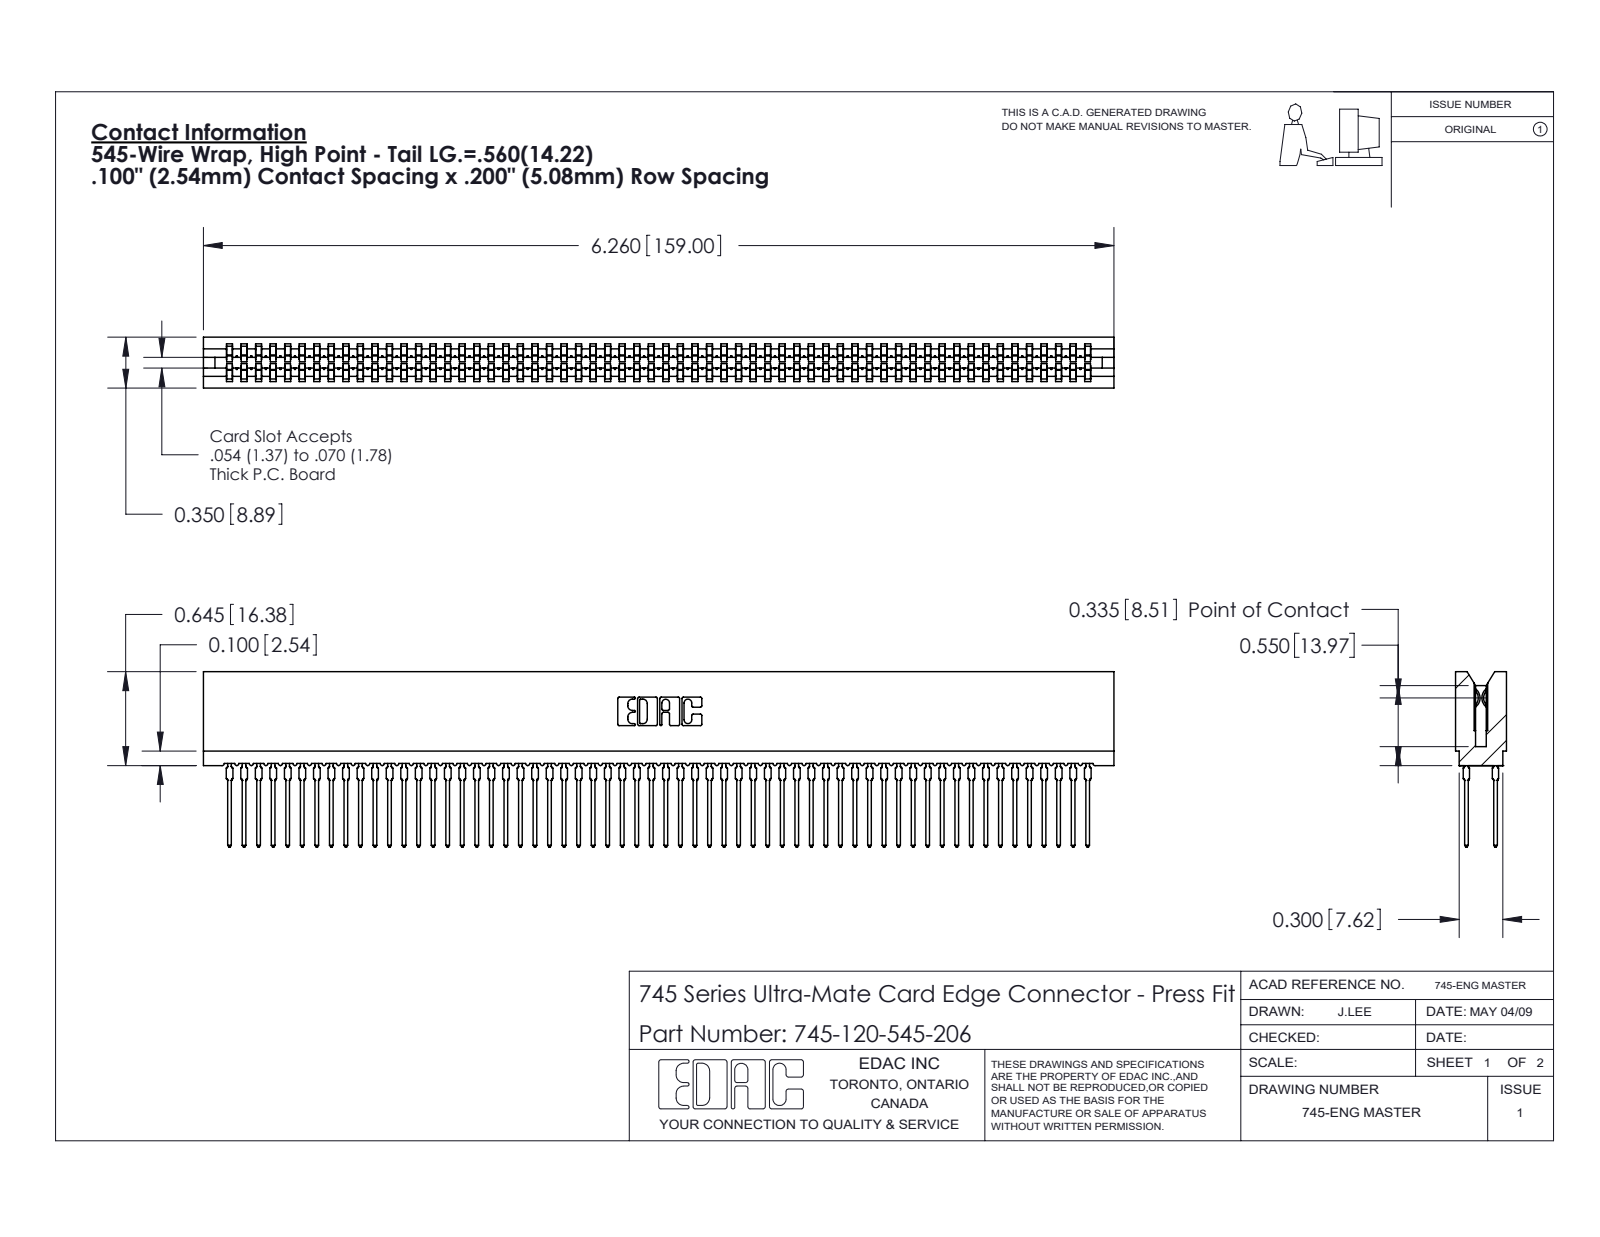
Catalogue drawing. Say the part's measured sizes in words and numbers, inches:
The part is named "745-292-001_545; 745-120-545-206; 745 Part_Insulator Option - 06". Its 3-D file was written by "SolidWorks 2020 (CONFIG_CONTROL_DESIGN)". It is 121 solids with 10836 faces: 5576 planar, 2140 cylindrical and 3120 other. Overall it measures 6.26 by 1.206 by 0.35 inches. Its volume is 0.892 cubic inches and its surface area 49.56 square inches. Partial cylindrical surfaces (rounded edges, fillets, slot ends): 240 of radius 0.021, 120 of radius 0.015, 22 of radius 0.01, 8 of radius 0.005, 8 of radius 0.011, 6 of radius 0.007, 6 of radius 0.031, 3 of radius 0.026. The main face-to-face distances are 0.063, 0.287, 0.35, 0.2, 0.045, 0.305, 0.018, 0.243, 0.138, 0.212.
